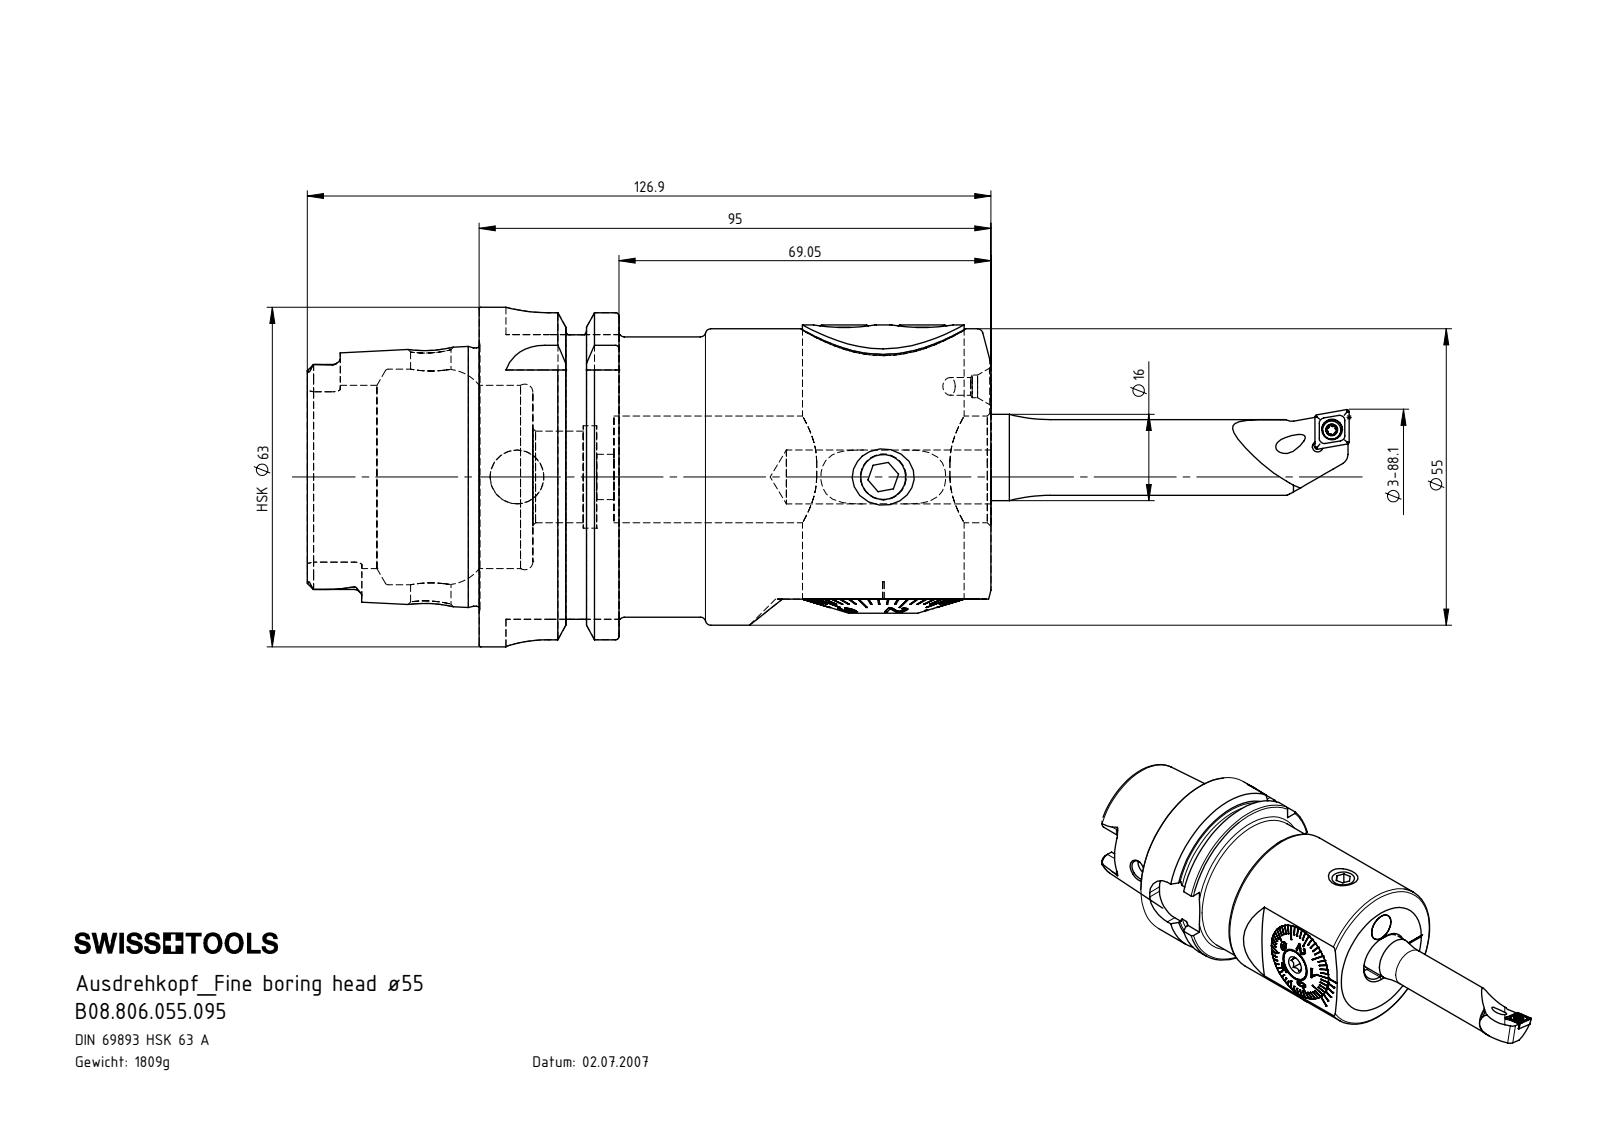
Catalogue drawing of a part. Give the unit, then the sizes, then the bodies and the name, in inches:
Units: inches
Overall size (bounding box): 4.996 × 2.48 × 2.48
Round holes (diameter × count): ⌀0.335 ×3, ⌀0.394 ×2, ⌀0.063 ×1, ⌀0.13 ×1, ⌀0.165 ×1, ⌀0.295 ×1, ⌀0.315 ×1, ⌀0.331 ×1, ⌀0.449 ×1, ⌀0.488 ×1, ⌀0.551 ×1, ⌀0.559 ×1
Round bosses / shafts (diameter × count): ⌀0.394 ×3, ⌀2.48 ×1, ⌀2.165 ×1, ⌀2.163 ×1, ⌀2.047 ×1, ⌀1.887 ×1, ⌀1.181 ×1, ⌀1.18 ×1
Partial cylindrical surfaces — rounded edges, fillets, slot ends (radius × count): R0.055 ×10, R0.013 ×6, R0.023 ×6, R0.02 ×4, R0.031 ×4, R0.075 ×4, R0.113 ×4, R0.315 ×4
Main face-to-face distances: 3.74, 0.63, 1.022, 2.719, 0.209, 0.392, 3.348, 0.256, 0.11, 0.098
Hole centre spacings: 0.571, 0.285, 0.014, 0.741, 0.754, 1.121, 2.677, 3.022
Volume: 13.05 in³ · Surface area: 88.26 in²
Bodies: 16 solids, 887 faces (367 planar, 178 cylindrical, 342 other)
Part name (STEP PRODUCT): DIN 3771 - 17x2; DIN 3771 - 25x1.5; Klebstoff D10; WCB-ER2.001.009_A (+8 more)
STEP written by: SolidWorks 2017 (CONFIG_CONTROL_DESIGN)
